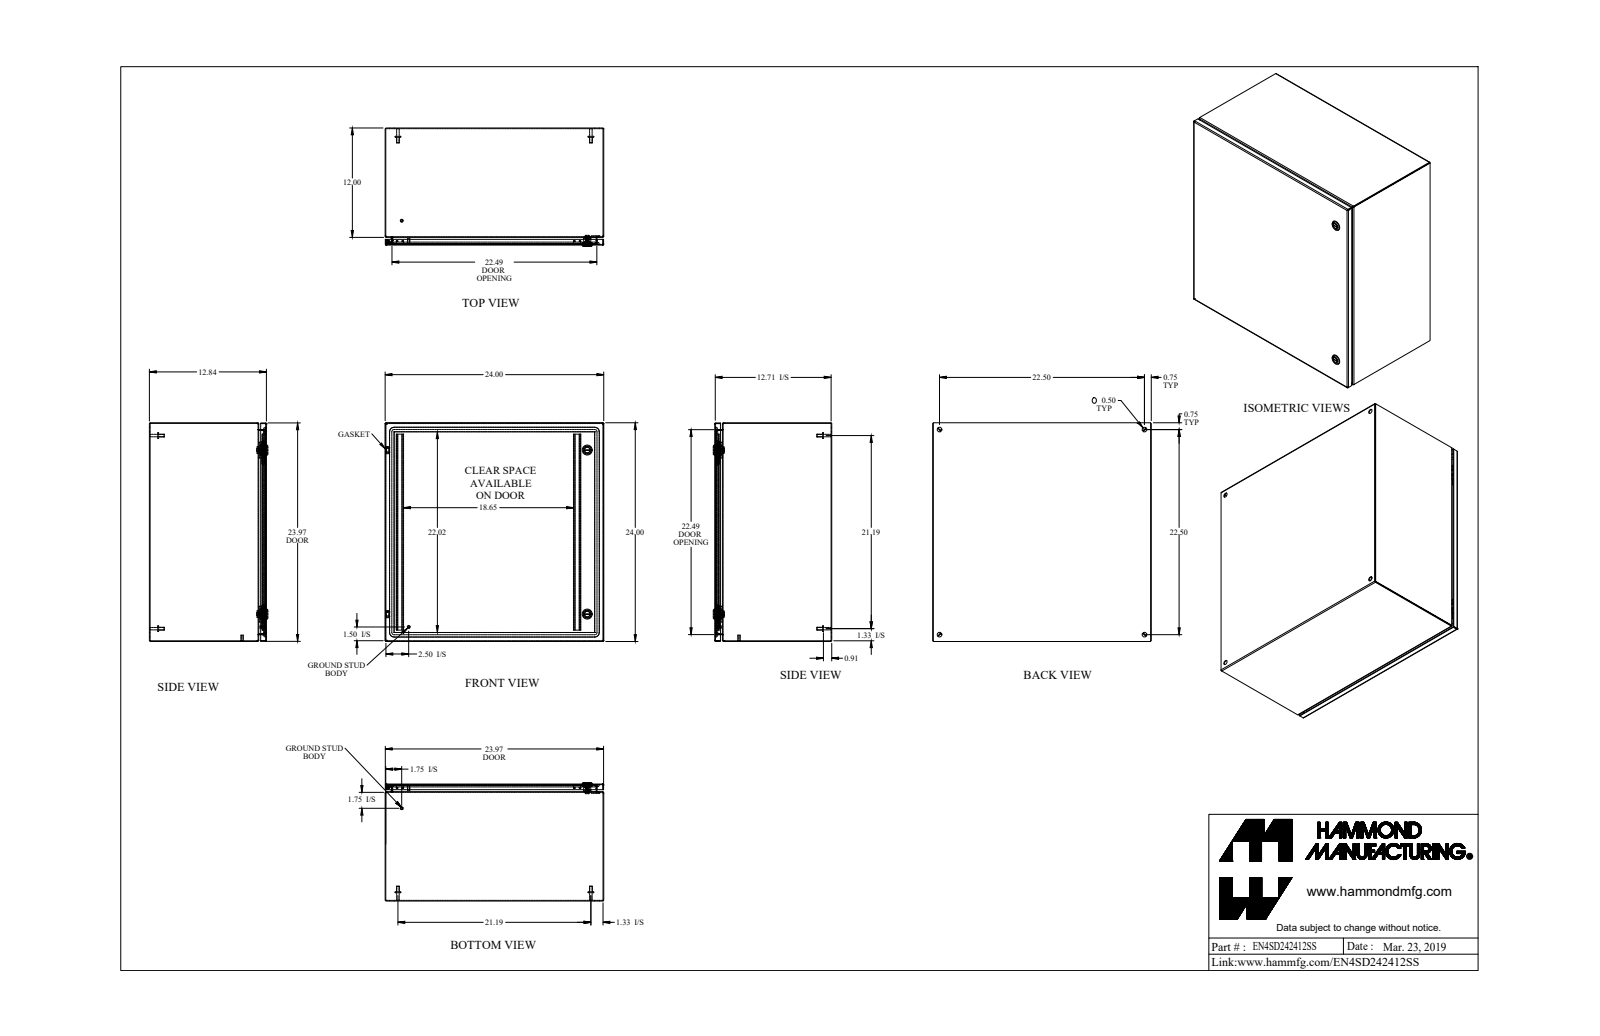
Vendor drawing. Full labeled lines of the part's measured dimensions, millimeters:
Part name (STEP PRODUCT): EN4SD242412SS
STEP written by: SolidWorks 2019 (AUTOMOTIVE_DESIGN)
Units: millimetres
Bodies: 31 solids, 774 faces (383 planar, 259 cylindrical, 132 other)
Overall size (bounding box): 609.6 × 609.6 × 330.3
Volume: 3 135 000 mm³ · Surface area: 3 463 000 mm²
Round holes (diameter × count): ⌀12.7 ×6, ⌀5 ×2, ⌀9.8 ×2, ⌀16 ×2, ⌀19.5 ×2, ⌀4.4 ×1, ⌀6.1 ×1, ⌀6.1 ×1
Round bosses / shafts (diameter × count): ⌀8 ×6, ⌀15.9 ×4, ⌀7 ×4, ⌀27.9 ×2, ⌀19.9 ×2, ⌀15.9 ×2, ⌀13.3 ×2, ⌀6.4 ×2
Partial cylindrical surfaces — rounded edges, fillets, slot ends (radius × count): R0.9 ×14, R2.7 ×14, R0.3 ×12, R1.2 ×12, R7.9 ×12, R2.5 ×8, R0.2 ×4, R1.6 ×4
Main face-to-face distances: 1.8, 324.4, 607.8, 322.5, 605.9, 326.2, 609.6, 21.4, 303, 19.1
Hole centre spacings: 571.5, 547.5, 808.2, 63.2, 63.2, 457.2, 515.1, 515.1
